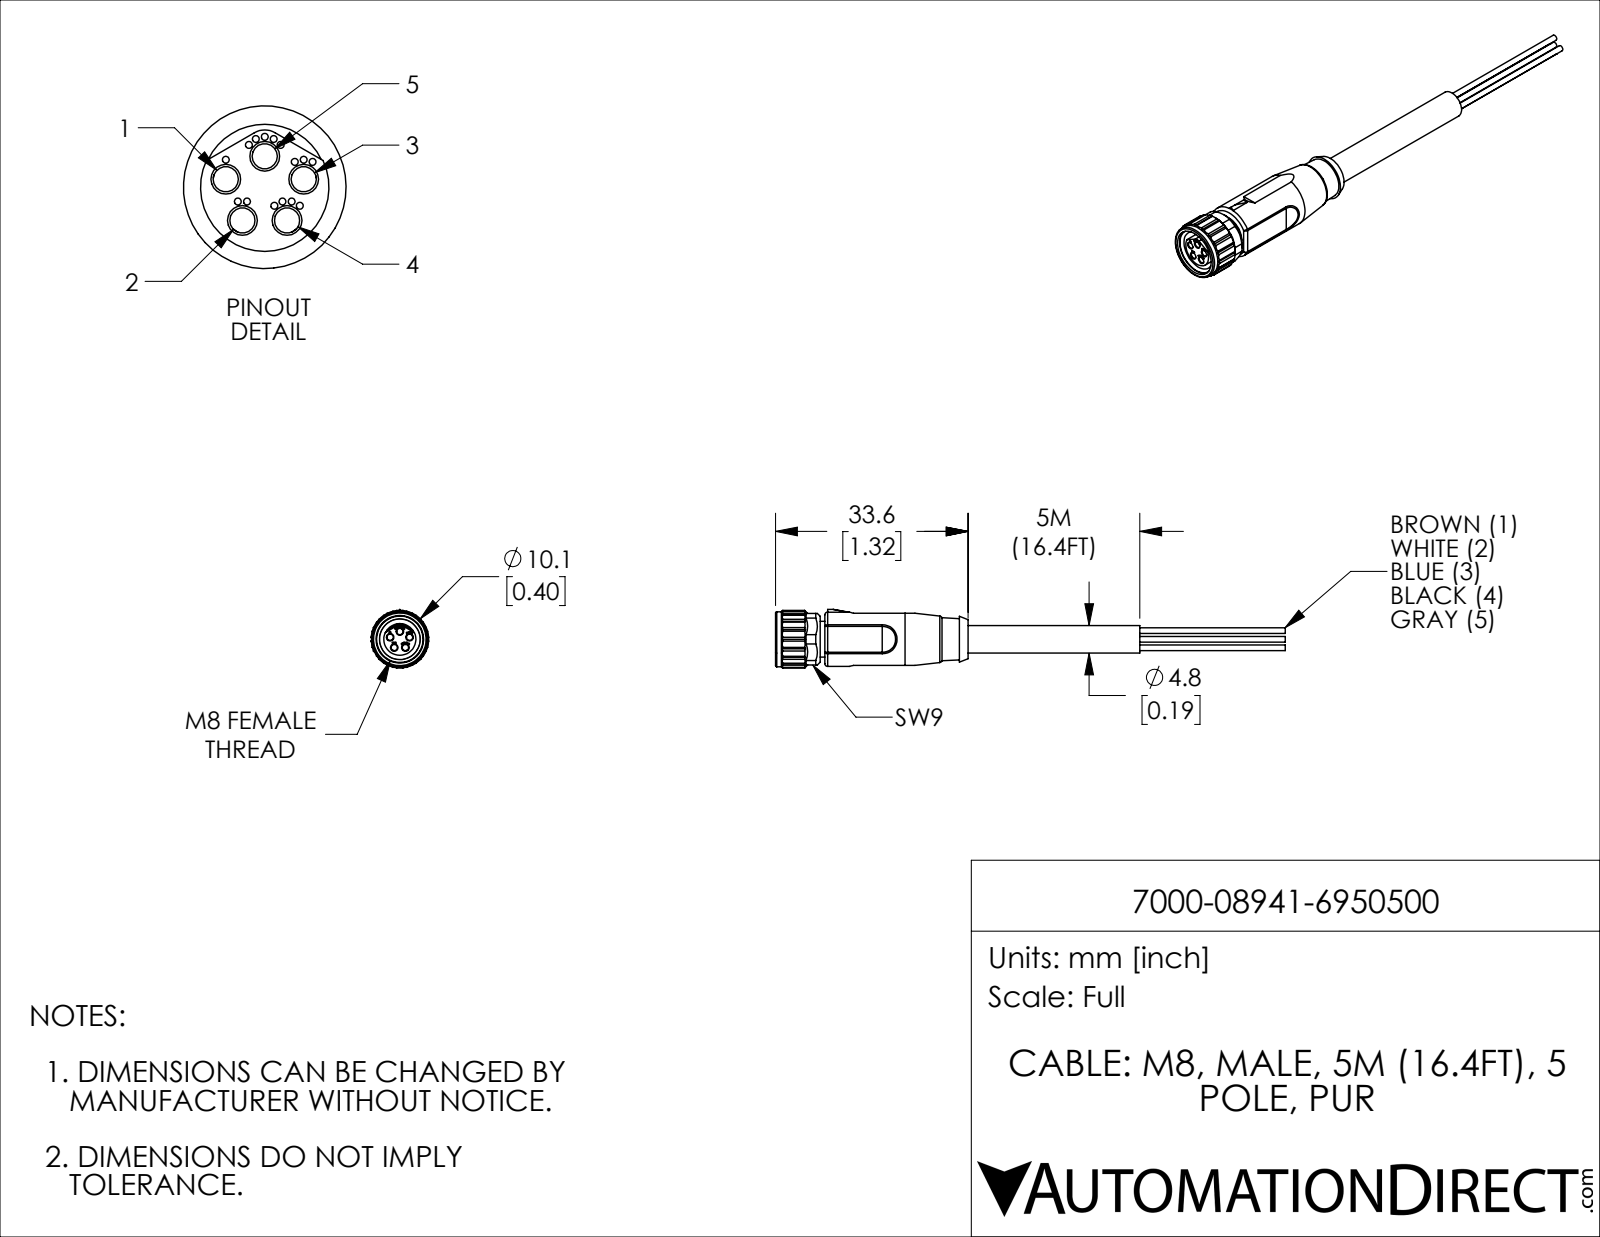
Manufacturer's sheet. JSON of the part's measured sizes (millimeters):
{"part_name": "7000-08941-6950500", "step_written_by": "SolidWorks 2019 (CONFIG_CONTROL_DESIGN)", "units": "millimeters", "bodies": {"solids": 1, "faces": 285, "planar": 111, "cylindrical": 127, "other": 47}, "overall_size": [89, 10.2, 10.1], "volume_mm3": 2620, "surface_area_mm2": 2297, "round_holes": [[0.3, 15], [1.1, 5], [6.1, 1], [7.1, 1], [8.3, 1]], "round_bosses_or_shafts": [[1, 5], [9.6, 1], [9.5, 1], [6.2, 1], [4.8, 1]], "partial_cylinders_radius": [[2, 18], [0.5, 6], [0.8, 6], [0.8, 4], [0.2, 2], [5, 2], [0.9, 1], [2.3, 1]], "face_to_face_distances": [8.2, 9.1, 9.1, 0.8, 25.8, 25, 9, 7.1, 7.9, 32.9], "hole_center_spacings": [0.8, 0.4, 2, 0.8, 1.1, 1.8, 2, 2.5]}
